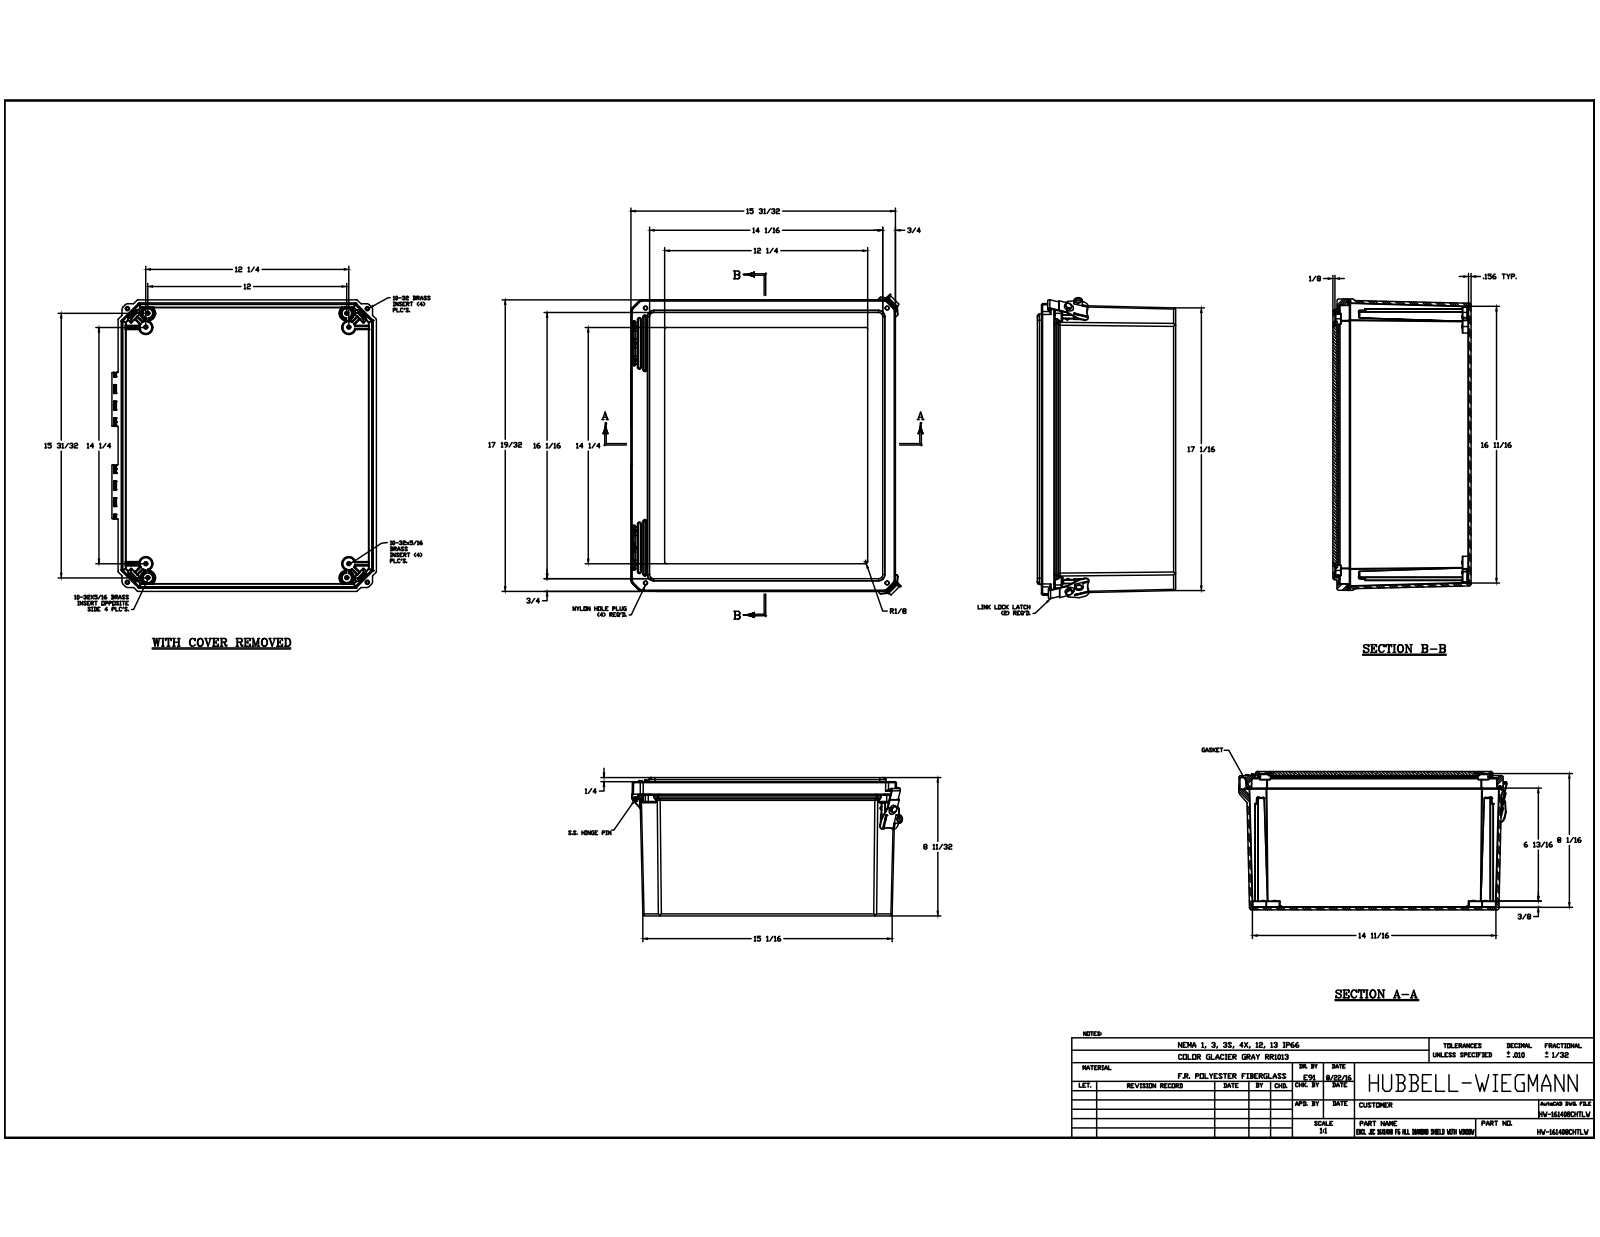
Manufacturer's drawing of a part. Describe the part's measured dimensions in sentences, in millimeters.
The part is named "DSW161408HLL_STP; DS161408BOX; BRASS INSERT-(; BRASS INSERT-(_1 (+7 more)". Its 3-D file was written by "Autodesk Inventor 2017 (AUTOMOTIVE_DESIGN)". It is 36 solids with 2374 faces: 826 planar, 932 cylindrical and 616 other. Overall it measures 469.14 by 416.69 by 211.92 millimeters. Its volume is 3 345 000 cubic millimeters and its surface area 1 486 000 square millimeters. Round holes: 16 of diameter 3.96, 8 of diameter 3.86, 4 of diameter 2.49, 4 of diameter 3.81, 4 of diameter 6.4, 4 of diameter 6.43, 2 of diameter 1.27, 2 of diameter 3.05, 2 of diameter 5.56, 2 of diameter 5.77, 2 of diameter 7.94, 2 of diameter 9.22. Round bosses or shafts: 16 of diameter 6.25, 4 of diameter 5.3, 4 of diameter 5.08, 3 of diameter 3.43, 3 of diameter 1.27, 2 of diameter 15.24, 1 of diameter 11.05, 1 of diameter 11.05. Partial cylindrical surfaces (rounded edges, fillets, slot ends): 195 of radius 0.25, 80 of radius 0.13, 57 of radius 0.51, 45 of radius 0.76, 38 of radius 3.17, 28 of radius 0.99, 26 of radius 1.59, 24 of radius 0.76. The main face-to-face distances are 3.96, 4.56, 4.59, 206.21, 202.25, 211.92, 207.96, 5.71, 3.17, 6.35. The hole center spacings are 519.13, 21.98, 41.94, 308.74, 342.1, 383.7, 392.71, 33.78.
